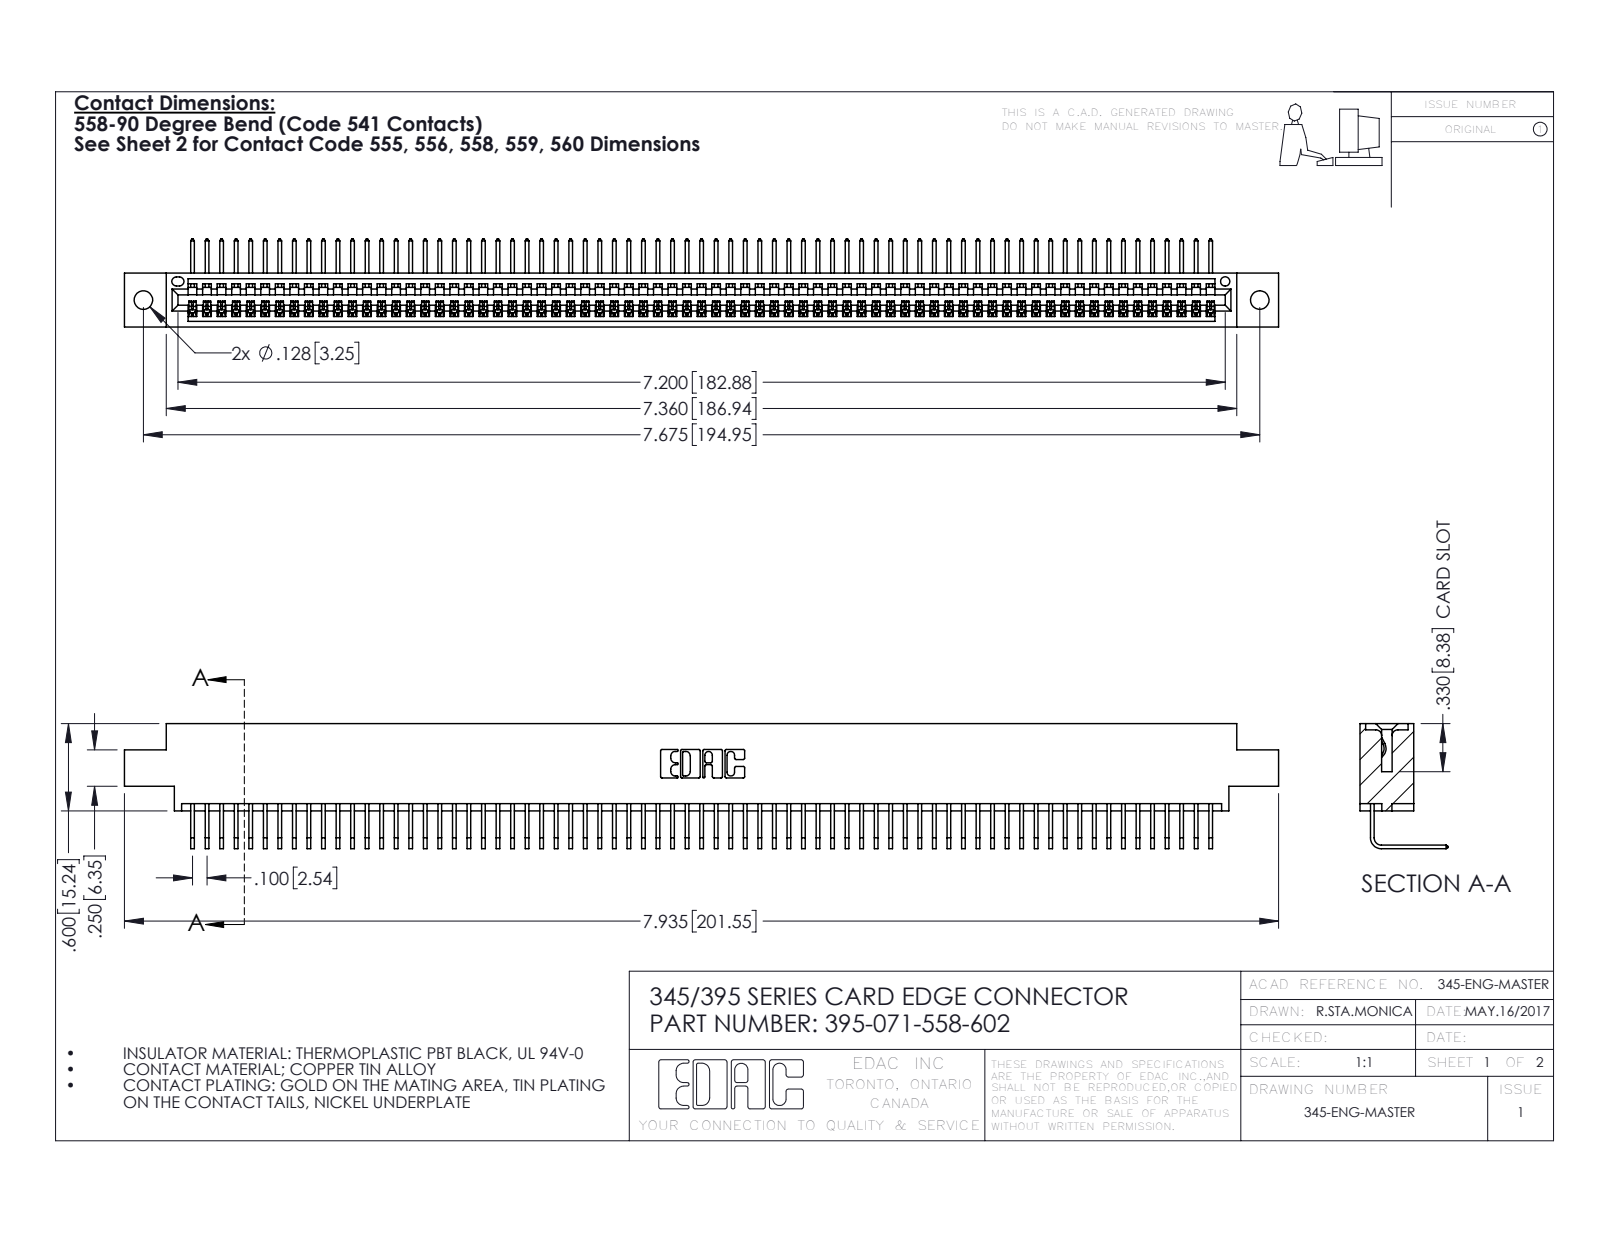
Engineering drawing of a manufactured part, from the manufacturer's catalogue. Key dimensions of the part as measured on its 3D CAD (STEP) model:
Part name (STEP PRODUCT): 345-292-001_558 Tail - 2; 345 Part_0.170 Offset - 0.128 Dia; 395-071-558-602
STEP written by: SolidWorks 2016 (CONFIG_CONTROL_DESIGN)
Units: inches
Bodies: 72 solids, 4390 faces (3066 planar, 1324 cylindrical, 0 other)
Overall size (bounding box): 7.935 × 0.859 × 0.605
Volume: 1.188 in³ · Surface area: 42.64 in²
Round holes (diameter × count): ⌀0.128 ×2, ⌀0.064 ×1
Partial cylindrical surfaces — rounded edges, fillets, slot ends (radius × count): R0.006 ×142, R0.01 ×22, R0.007 ×6, R0.031 ×6, R0.026 ×3, R0.031 ×2, R0.04 ×2, R0.014 ×1
Main face-to-face distances: 0.072, 0.298, 0.37, 0.2, 0.098, 0.272, 0.025, 0.225, 0.175, 0.149
Hole centre spacings: 0.27, 7.439, 7.675
